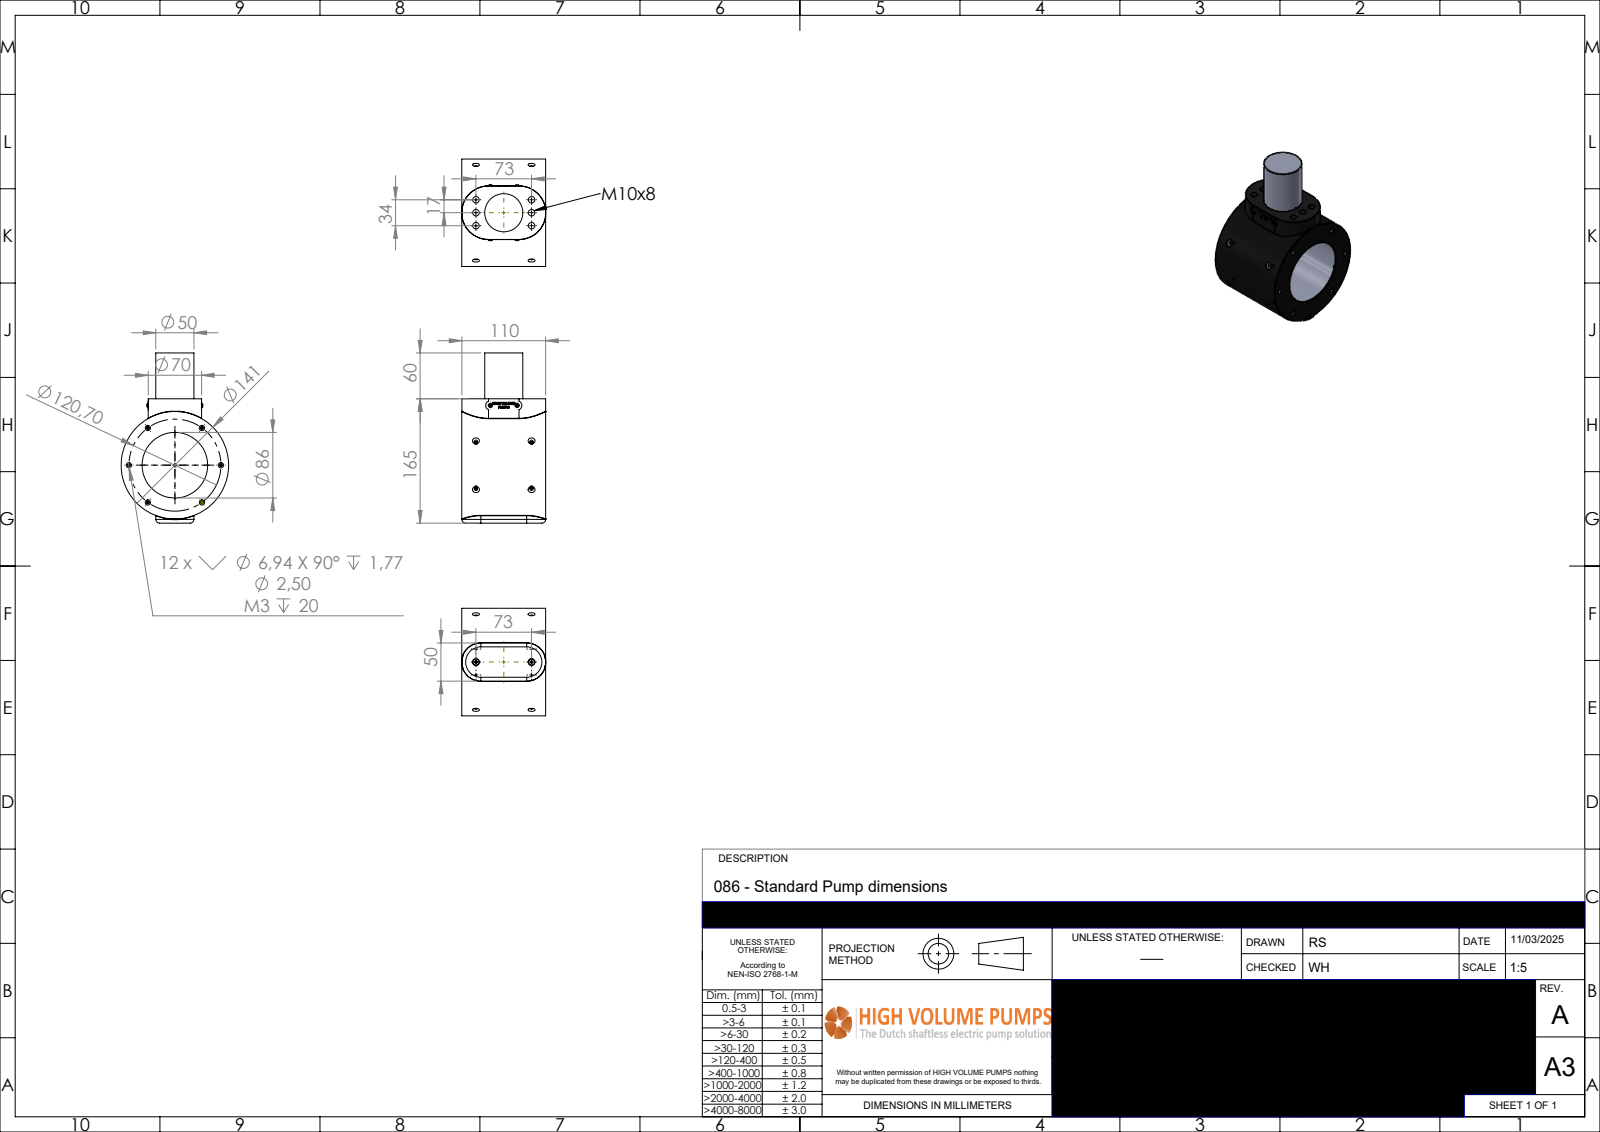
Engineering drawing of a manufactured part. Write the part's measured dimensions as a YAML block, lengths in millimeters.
part_name: "P-086-030-rev-A-SP"
step_written_by: "SolidWorks 2024 (AUTOMOTIVE_DESIGN)"
units: millimeters
bodies: {solids: 1, faces: 630, planar: 373, cylindrical: 57, other: 200}
overall_size: [223.22, 141, 110.06]
volume: 1351000
surface_area: 120685
round_holes:
  - {diameter: 2.5, count: 6}
  - {diameter: 8.5, count: 6}
  - {diameter: 3.3, count: 4}
  - {diameter: 4.5, count: 4}
  - {diameter: 86, count: 1}
round_bosses_or_shafts:
  - {diameter: 7.64, count: 2}
  - {diameter: 5.7, count: 2}
  - {diameter: 141, count: 1}
  - {diameter: 50, count: 1}
partial_cylinders:
  - {radius: 0.5, count: 4}
  - {radius: 5, count: 2}
  - {radius: 6.25, count: 2}
  - {radius: 25, count: 2}
  - {radius: 35, count: 2}
face_to_face_distances: [110.06, 163.22, 60, 223.22, 70, 10, 153.78, 9.44, 69.44, 50]
hole_center_spacings: [73, 17, 60.35, 74.95, 107.54, 120.7, 34, 54.79]
